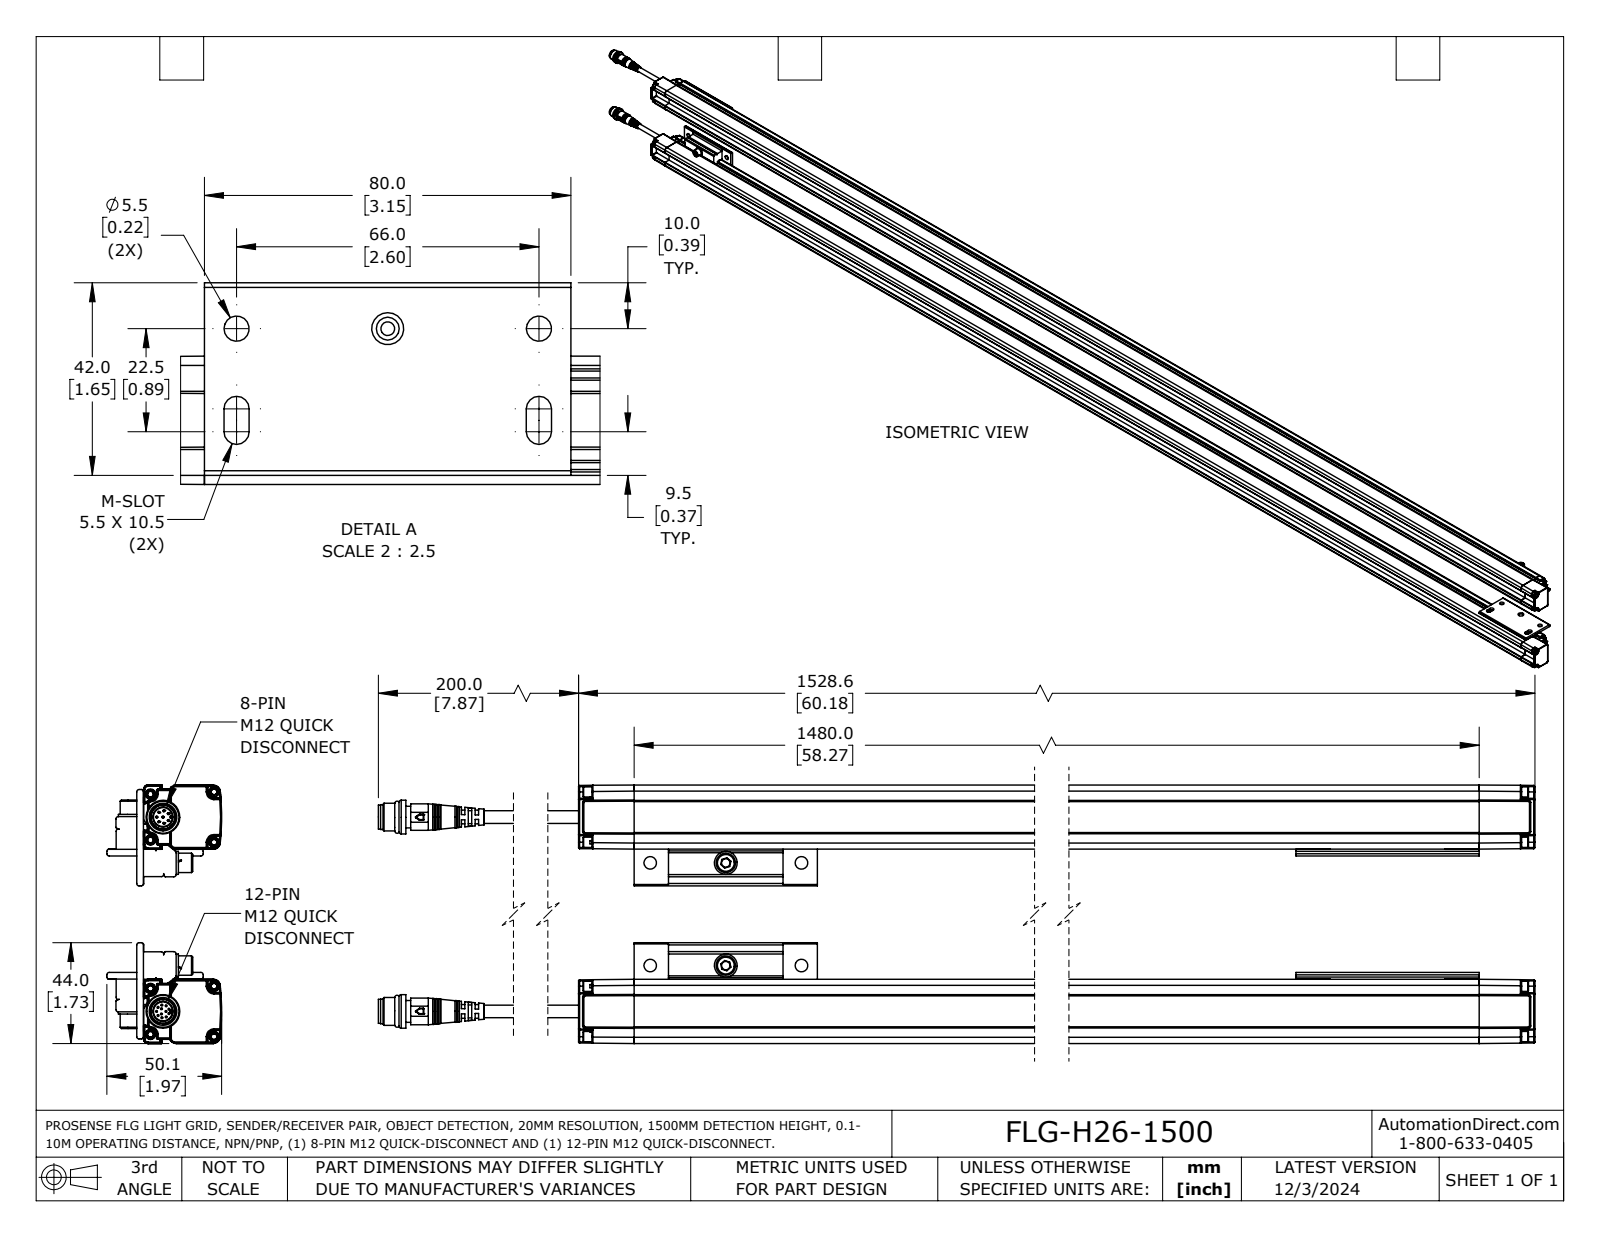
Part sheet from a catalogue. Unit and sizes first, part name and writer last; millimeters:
Units: millimetres
Overall size (bounding box): 1620.55 × 112.8 × 50.09
Round holes (diameter × count): ⌀0.4 ×16, ⌀5.5 ×6, ⌀2.5 ×4, ⌀5 ×3, ⌀8.3 ×2
Round bosses / shafts (diameter × count): ⌀0.8 ×20, ⌀4.5 ×8, ⌀3 ×8, ⌀5.5 ×4, ⌀1.5 ×4, ⌀10 ×3, ⌀8.5 ×3, ⌀3.7 ×3
Partial cylindrical surfaces — rounded edges, fillets, slot ends (radius × count): R0.5 ×142, R1 ×40, R0.25 ×20, R0.2 ×12, R0.3 ×12, R2.75 ×12, R2.55 ×6, R1.25 ×4
Main face-to-face distances: 84.8, 28, 1.8, 7.25, 20.75, 24.65, 56.8, 112.8, 26.45, 5.45
Hole centre spacings: 2.75, 33, 4.15, 24.87, 55.64, 5.45, 44.8, 66
Volume: 2 444 000 mm³ · Surface area: 592 431 mm²
Bodies: 10 solids, 1668 faces (816 planar, 456 cylindrical, 396 other)
Part name (STEP PRODUCT): FLG-H26-1500
STEP written by: SolidWorks 2023 (AUTOMOTIVE_DESIGN)
